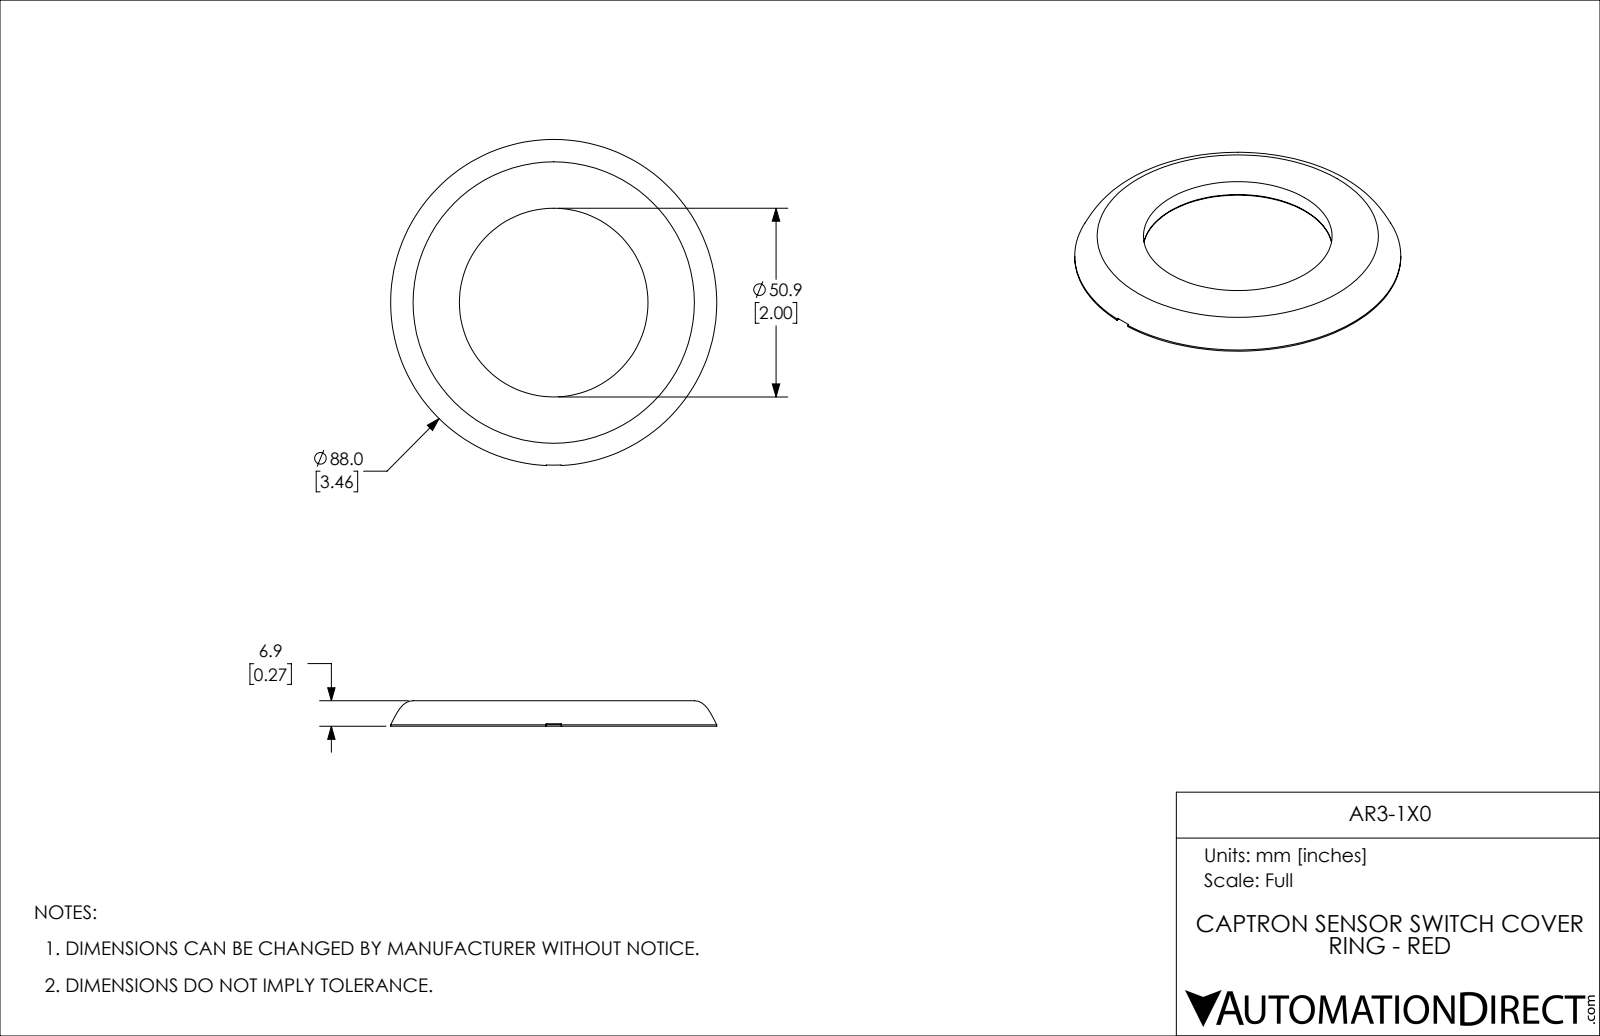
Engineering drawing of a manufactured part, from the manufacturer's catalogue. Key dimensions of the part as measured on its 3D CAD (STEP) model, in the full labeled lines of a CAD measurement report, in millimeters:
Part name (STEP PRODUCT): AR3-1X0
STEP written by: SolidWorks 2019 (CONFIG_CONTROL_DESIGN)
Units: millimetres
Bodies: 1 solid, 54 faces (12 planar, 4 cylindrical, 38 other)
Overall size (bounding box): 88 × 88 × 6.9
Volume: 8 520 mm³ · Surface area: 11 250 mm²
Round holes (diameter × count): ⌀5 ×1
Round bosses / shafts (diameter × count): ⌀55.3 ×1
Main face-to-face distances: 1.6, 3.1, 4.7, 2.9, 4.5, 3, 2.8, 1.7, 1.8, 2
